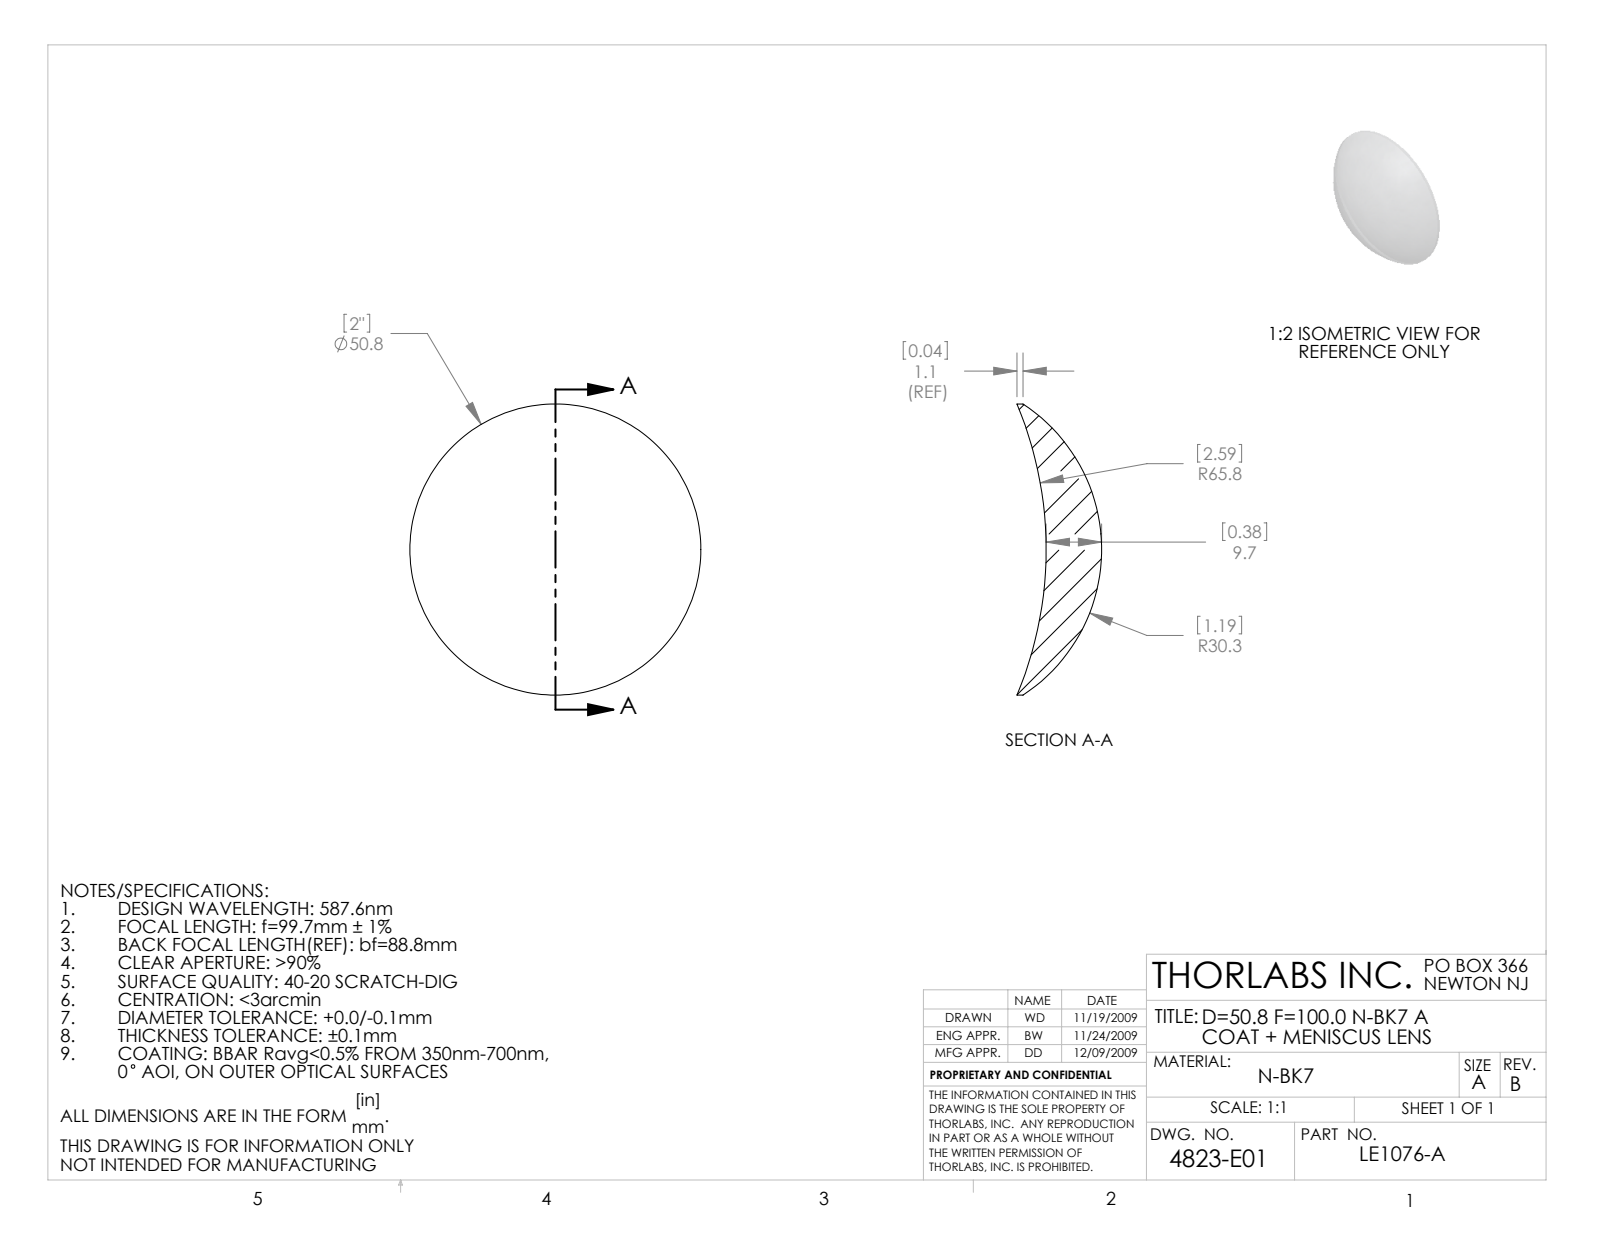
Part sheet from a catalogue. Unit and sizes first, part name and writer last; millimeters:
Units: millimetres
Overall size (bounding box): 50.8 × 50.8 × 14.8
Round bosses / shafts (diameter × count): ⌀50.8 ×1
Volume: 12 189 mm³ · Surface area: 4 897 mm²
Bodies: 1 solid, 6 faces (0 planar, 2 cylindrical, 4 other)
Part name (STEP PRODUCT): 4823-E0W
STEP written by: SolidWorks 2009 (AUTOMOTIVE_DESIGN)
